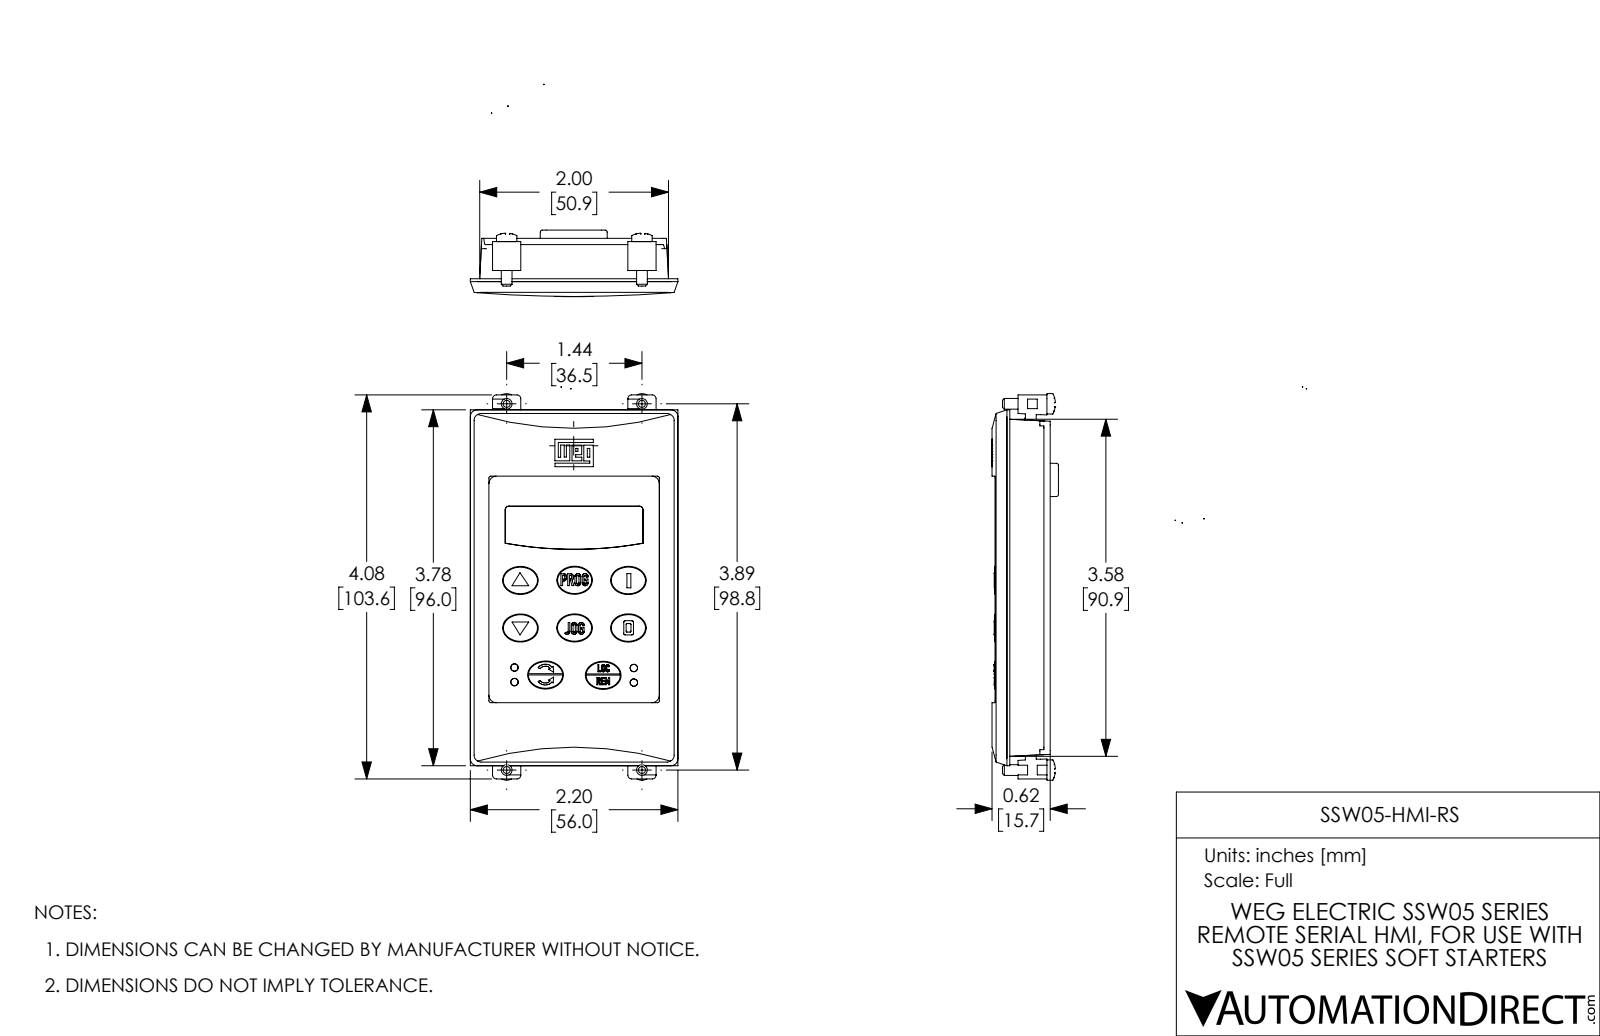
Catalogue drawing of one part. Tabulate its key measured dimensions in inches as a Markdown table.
| quantity | value |
| --- | --- |
| part name | SSW07-HMI-REM b1 |
| STEP written by | SolidWorks 2017 (AUTOMOTIVE_DESIGN) |
| units | inches |
| bodies | 65 solids, 2590 faces (1852 planar, 498 cylindrical, 240 other) |
| overall size | 4.177 × 3.345 × 2.205 |
| volume | 2.41 in³ |
| surface area | 86.04 in² |
| round holes (diameter × count) | 0.079 × 16, 0.327 × 8, 0.089 × 6, 0.118 × 6, 0.055 × 5, 0.071 × 4, 0.098 × 4, 0.102 × 4, 0.091 × 2 |
| round bosses / shafts (diameter × count) | 0.043 × 9, 0.138 × 8, 0.134 × 8, 0.118 × 8, 0.217 × 4, 0.15 × 4, 0.114 × 4, 0.098 × 4 |
| partial cylindrical surfaces (radius × count) | 0.004 × 32, 0.039 × 30, 0.016 × 16, 0.017 × 16, 0.02 × 16, 0.079 × 12, 0.1 × 8, 0.132 × 8 |
| main face-to-face distances | 0.067, 0.508, 0.575, 0.236, 0.339, 0.169, 0.516, 0.063, 0.069, 0.299 |
| hole center spacings | 0.505, 0.575, 1.147, 1.201, 1.252, 1.265, 1.276, 1.278 |
